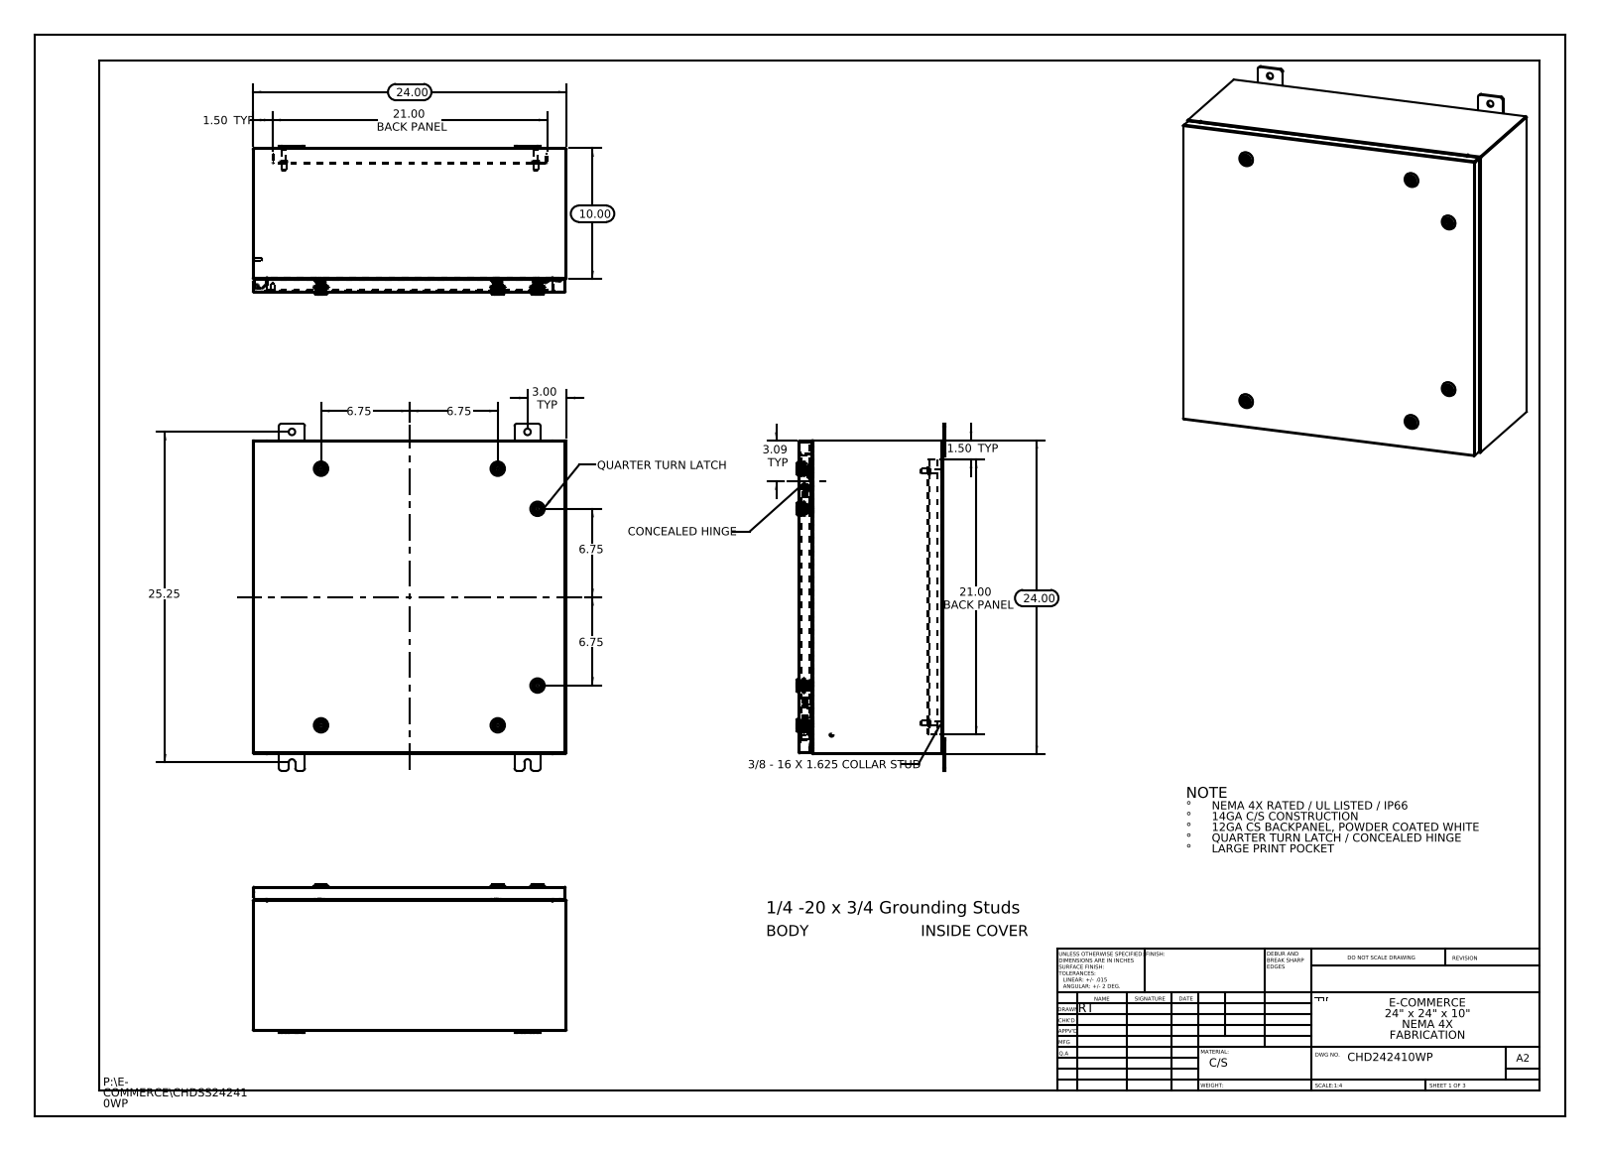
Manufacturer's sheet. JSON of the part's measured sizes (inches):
{"part_name": "Washer-221320-IB-Industrilas_Washer-221320-IB-Industrilas; CHDSS242410WP Bottom; CHDSS242410WP Backpanel; Concealed Hinge enclosure side (+8 more)", "step_written_by": "SolidWorks 2013 (CONFIG_CONTROL_DESIGN)", "units": "inches", "bodies": {"solids": 55, "faces": 5420, "planar": 1592, "cylindrical": 1692, "other": 2136}, "overall_size": [26.5, 24, 11.356], "volume_in3": 232.9, "surface_area_in2": 5836, "round_holes": [[0.5, 8], [0.197, 6], [0.394, 6], [0.4, 6], [0.63, 6], [0.787, 6], [0.136, 4], [0.211, 1]], "round_bosses_or_shafts": [[0.236, 8], [1.102, 6], [0.78, 6], [0.626, 6], [0.61, 6], [0.531, 6], [0.392, 6], [0.114, 6]], "partial_cylinders_radius": [[0.006, 198], [0.118, 198], [0.028, 72], [0.02, 24], [0.19, 24], [0.197, 24], [0.013, 20], [0.088, 18]], "face_to_face_distances": [0.075, 23.925, 0.074, 11.01, 10.935, 10.936, 10.861, 23.85, 24, 0.104], "hole_center_spacings": [13.5, 0.688, 1.858, 2.878, 3.065, 16.376, 16.815, 17.687]}
